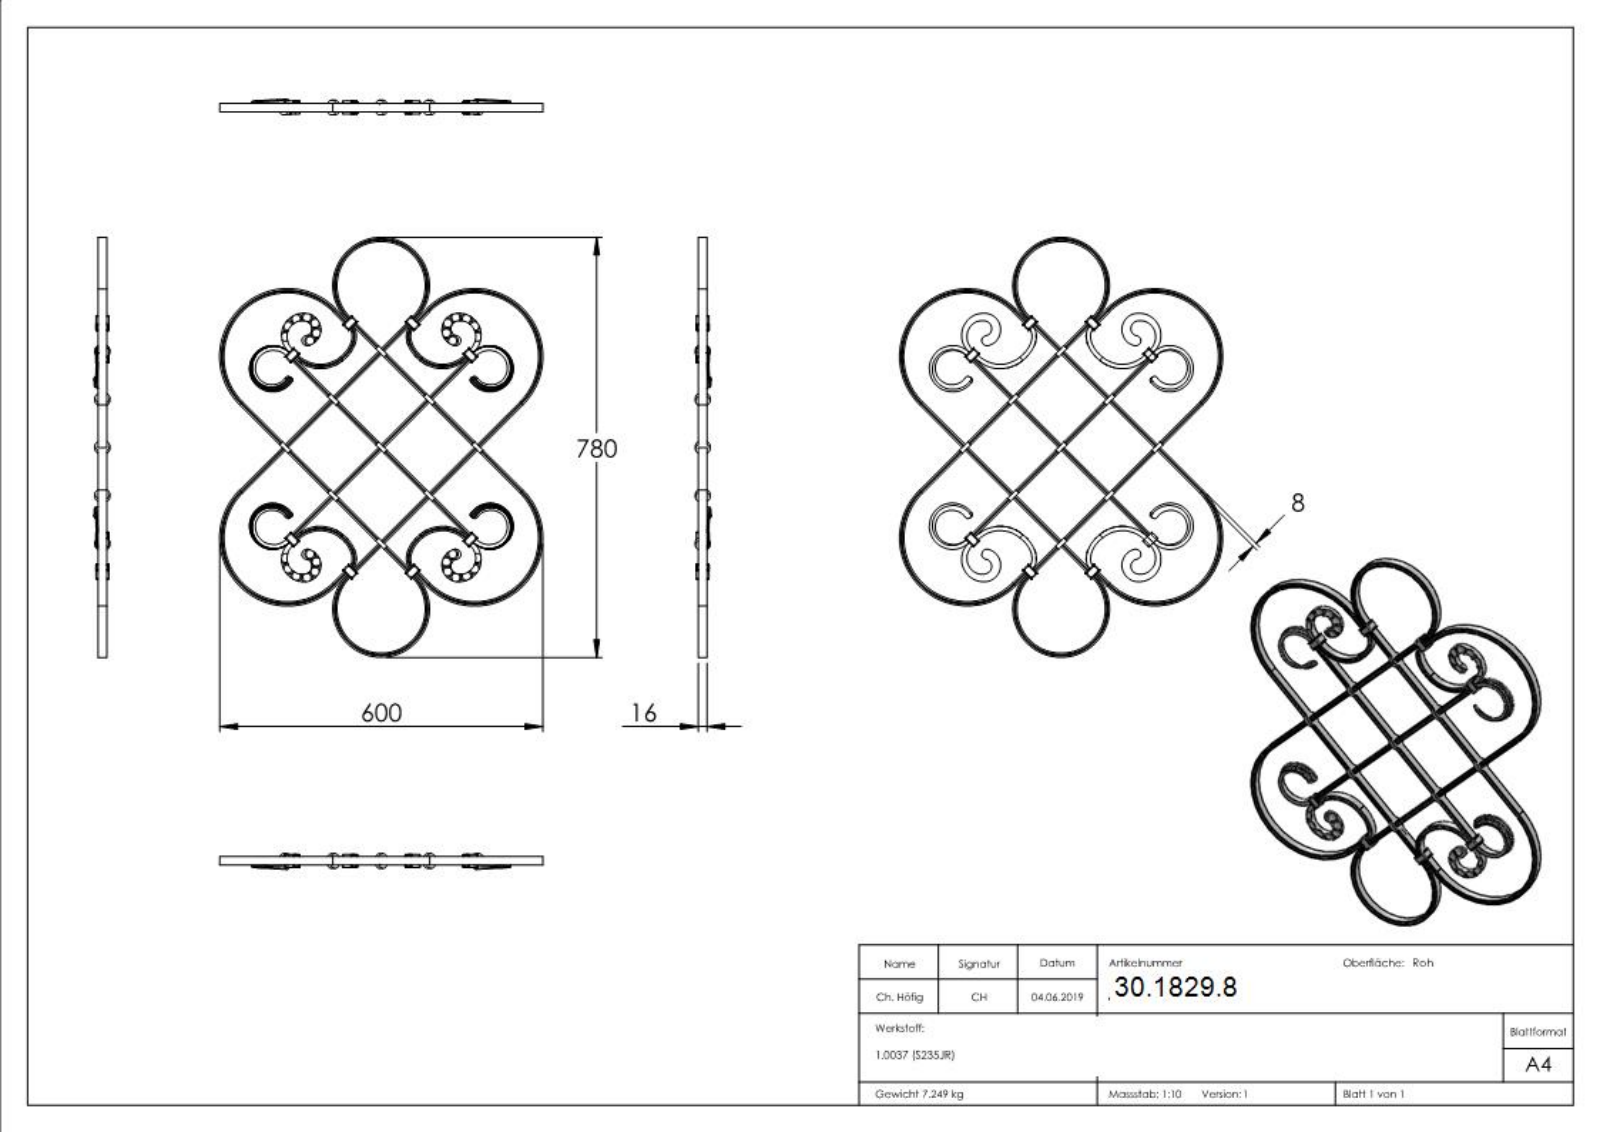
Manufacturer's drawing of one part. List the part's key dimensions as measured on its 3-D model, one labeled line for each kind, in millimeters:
Part name (STEP PRODUCT): 5017
STEP written by: SolidWorks 2015 (CONFIG_CONTROL_DESIGN)
Units: millimetres
Bodies: 21 solids, 1321 faces (680 planar, 206 cylindrical, 435 other)
Overall size (bounding box): 780 × 600 × 29.62
Volume: 929 491 mm³ · Surface area: 408 414 mm²
Partial cylindrical surfaces — rounded edges, fillets, slot ends (radius × count): R1 ×64, R2 ×53, R13.25 ×32, R13.75 ×9, R118.08 ×4, R126.08 ×4, R82 ×2, R90 ×2
Main face-to-face distances: 126.11, 8, 16, 134.11, 118.11, 252.22, 260.22, 244.22, 6, 218.34
